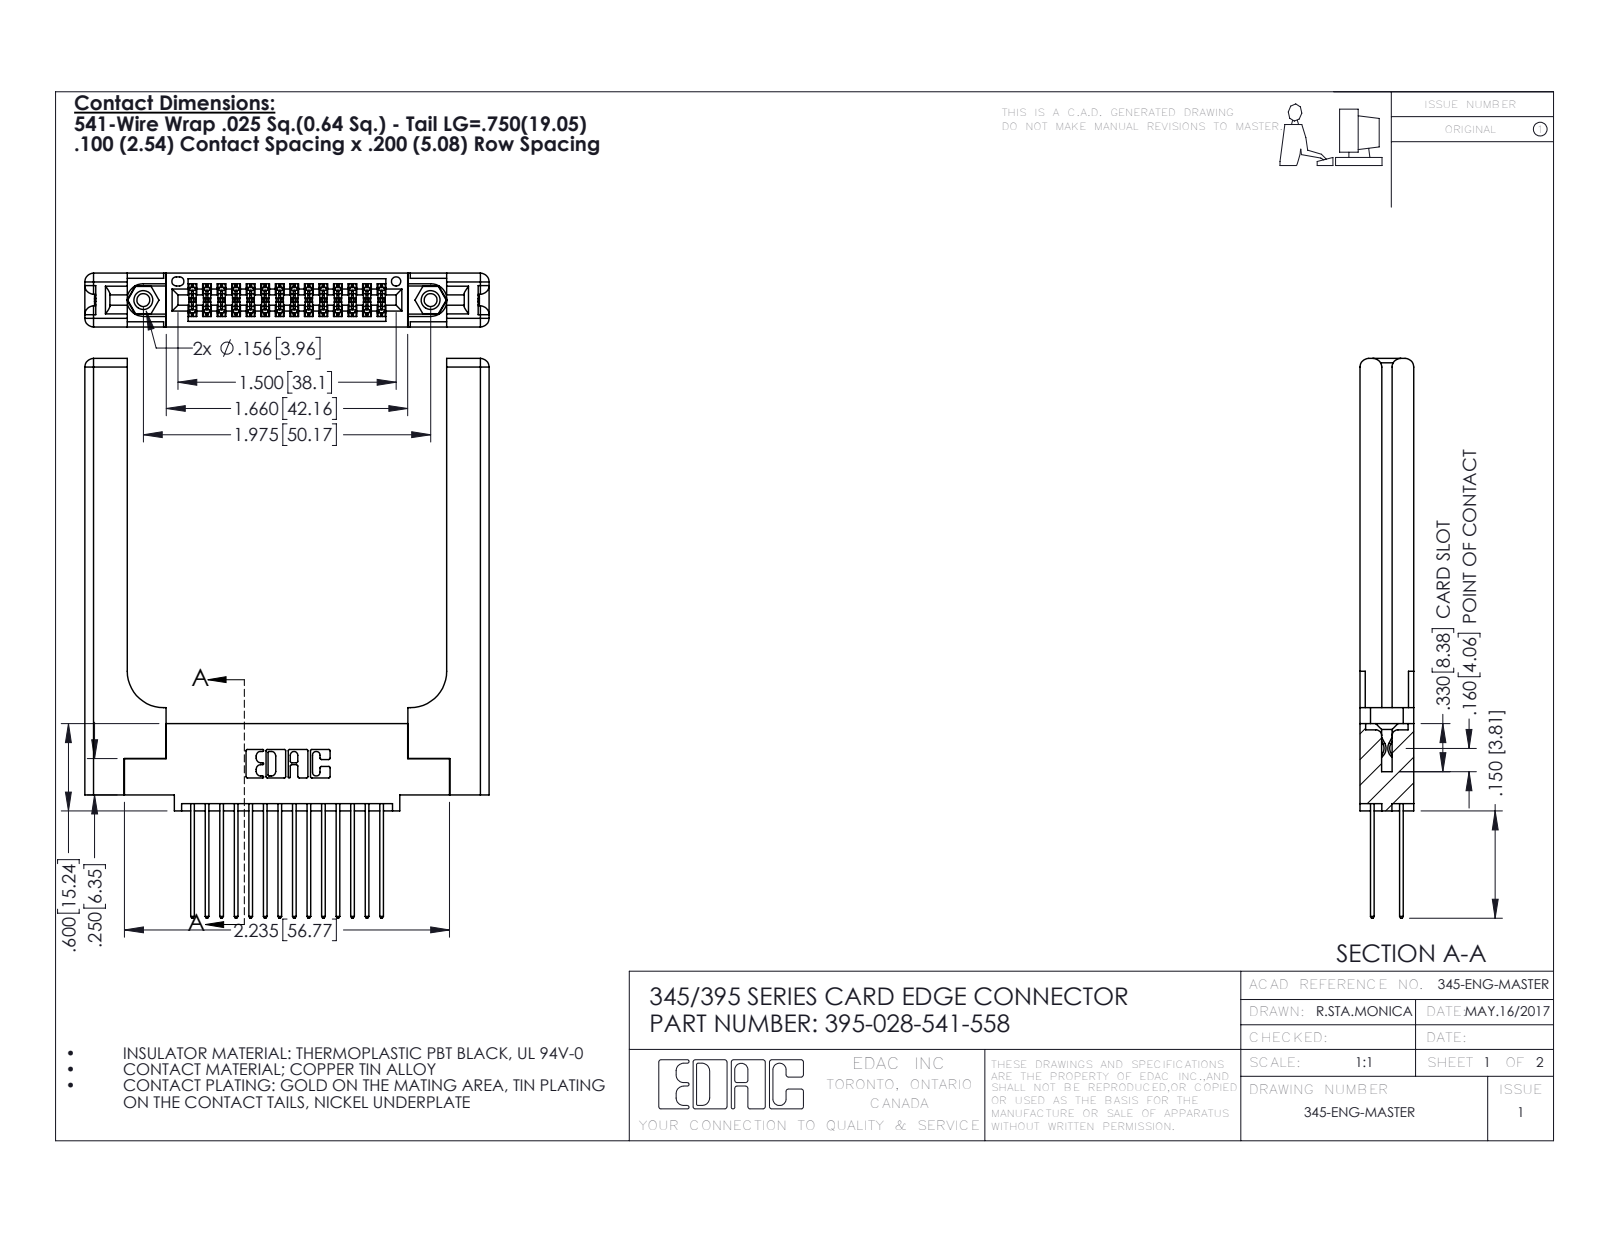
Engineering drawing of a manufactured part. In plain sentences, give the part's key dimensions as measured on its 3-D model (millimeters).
The part is named "345-220-058_345-220-058; 345 Part_0.110 Offset - 0.156 Dia-TH; 345-292-001_345-293-141; 395-028-541-558 (+1 more)". Its 3-D file was written by "SolidWorks 2016 (CONFIG_CONTROL_DESIGN)". It is 33 solids with 1786 faces: 1156 planar, 570 cylindrical and 60 other. Overall it measures 97.7 by 70.6 by 9.4 millimeters. Its volume is 15 200 cubic millimeters and its surface area 15 250 square millimeters. Round holes: 2 of diameter 2.3, 2 of diameter 3.2, 2 of diameter 4, 1 of diameter 1.6. Round bosses or shafts: 2 of diameter 3.9. Partial cylindrical surfaces (rounded edges, fillets, slot ends): 42 of radius 0.2, 28 of radius 0.3, 22 of radius 0.3, 16 of radius 1.5, 6 of radius 0.2, 6 of radius 0.8, 3 of radius 0.7, 2 of radius 0.4. The main face-to-face distances are 9.4, 1.8, 7.6, 5.1, 3.8, 3.8, 2, 2.5, 6.9, 0.6. The hole center spacings are 6.9, 44.2, 50.2.
